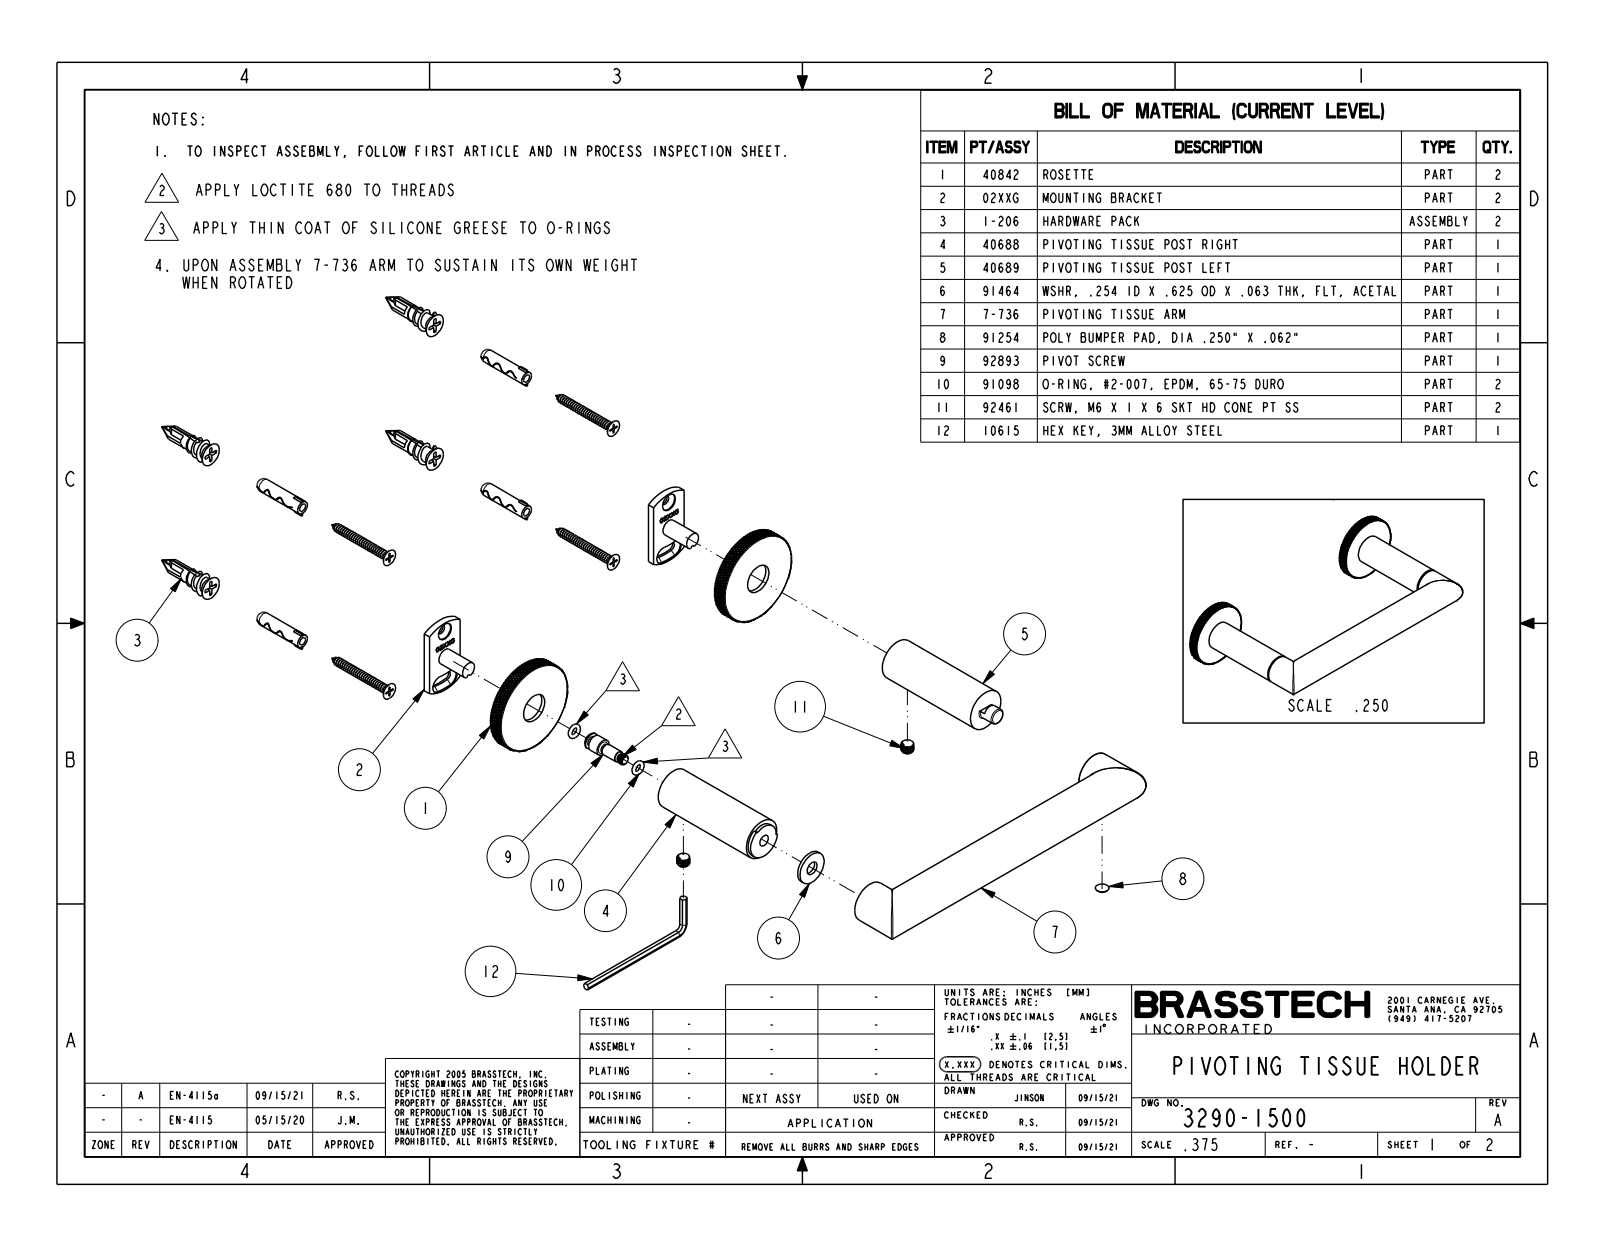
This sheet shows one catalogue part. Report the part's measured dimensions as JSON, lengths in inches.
{"part_name": "3290-1500", "step_written_by": "CREO PARAMETRIC BY PTC INC, 2018400 (CONFIG_CONTROL_DESIGN)", "units": "inches", "bodies": {"solids": 1, "faces": 6142, "planar": 17, "cylindrical": 1397, "other": 4728}, "overall_size": [7.55, 3.539, 1.75], "volume_in3": 6.806, "surface_area_in2": 42.43, "round_bosses_or_shafts": [[0.787, 3], [1.75, 2]], "partial_cylinders_radius": [[0.005, 5], [0.03, 3], [0.01, 2], [0.04, 2], [0.15, 1], [0.313, 1], [0.347, 1]], "face_to_face_distances": [0.26, 2.54, 2.28, 2.572, 2.312, 0.032, 2.922, 2.662, 0.382, 0.35]}
